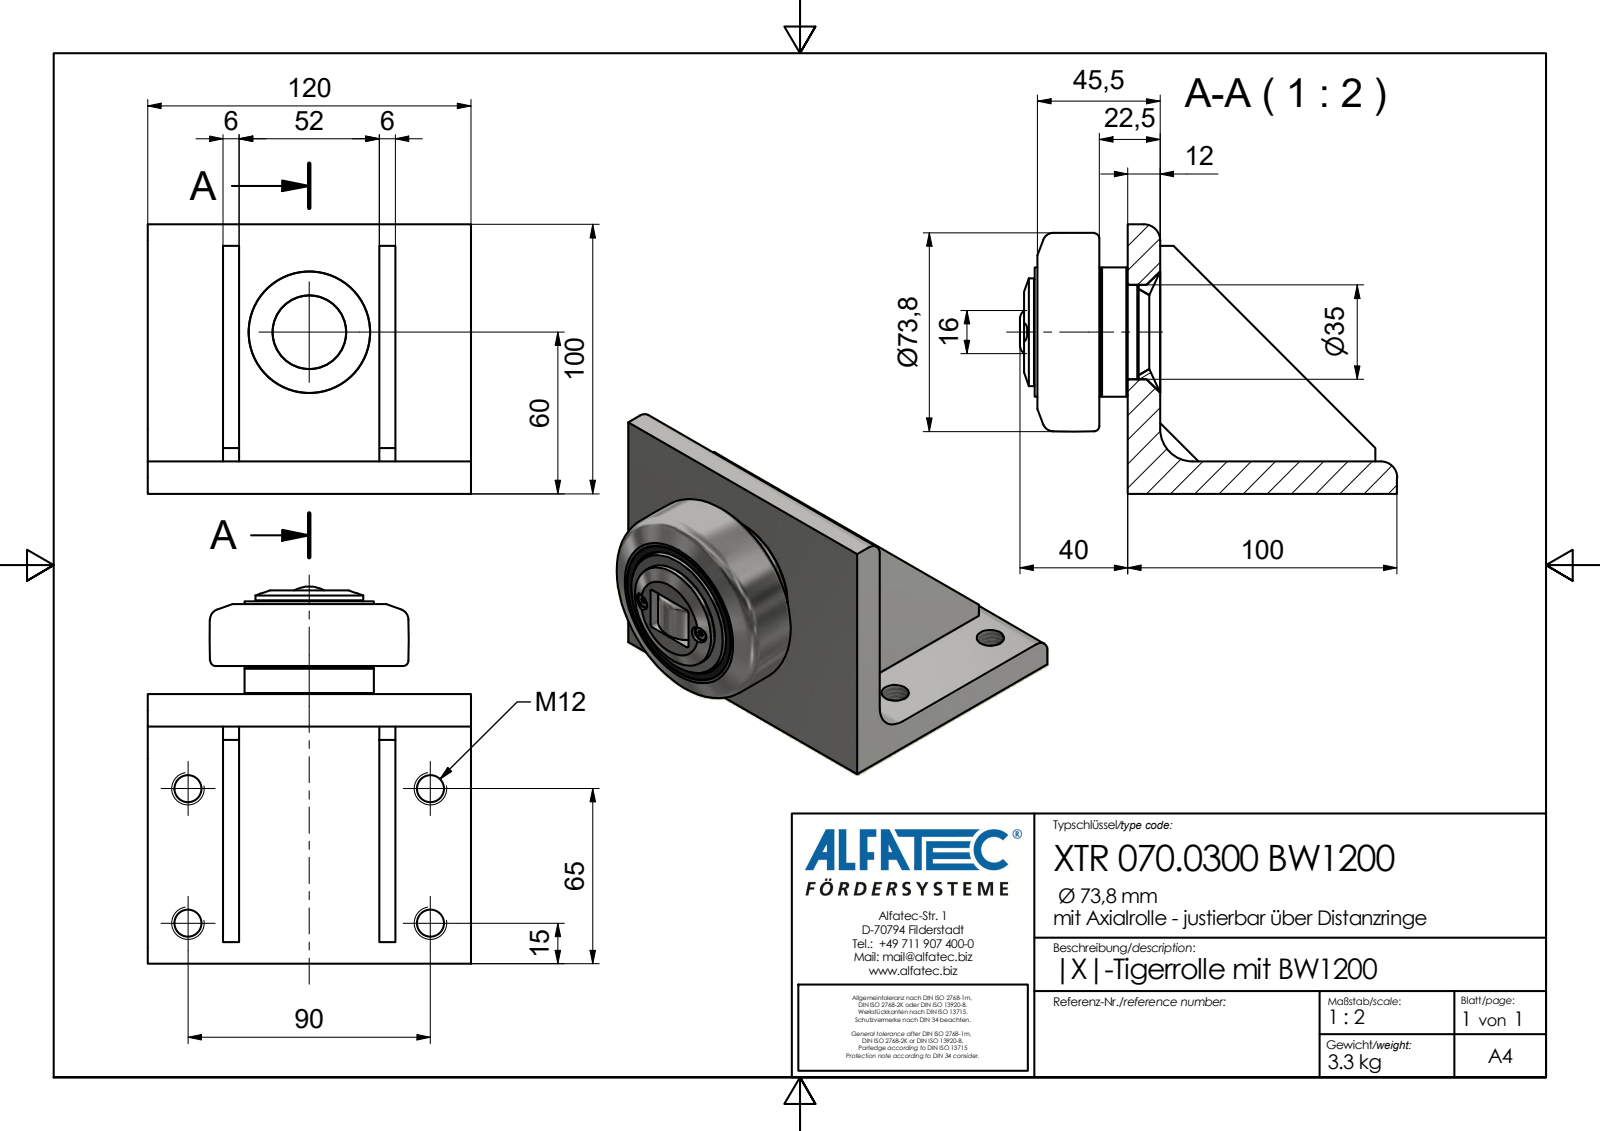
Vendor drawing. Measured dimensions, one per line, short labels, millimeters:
name: XTR 070.0300 BW1200_Kontur
written by: Autodesk Inventor 2020 (AP242_MANAGED_MODEL_BASED_3D_ENGINEERING_MIM_LF)
unit: mm
bodies: 1 solid, 125 faces (59 planar, 41 cylindrical, 25 other)
size: 140 × 120 × 100
volume: 425 932 mm³; area: 79 831 mm²
holes: 4× ⌀10.11, 2× ⌀3.5, 2× ⌀6.5, 1× ⌀25, 1× ⌀35.2
bosses: 2× ⌀5.35, 2× ⌀3, 1× ⌀48, 1× ⌀40, 1× ⌀35
rounds: 4× R1, 2× R6, 1× R5.1, 1× R5.5, 1× R6.5, 1× R8, 1× R12, 1× R12.47
face distances: 12, 6, 58, 92, 28, 34, 86, 52, 64, 120
hole spacings: 15, 50, 90, 102.96, 30
